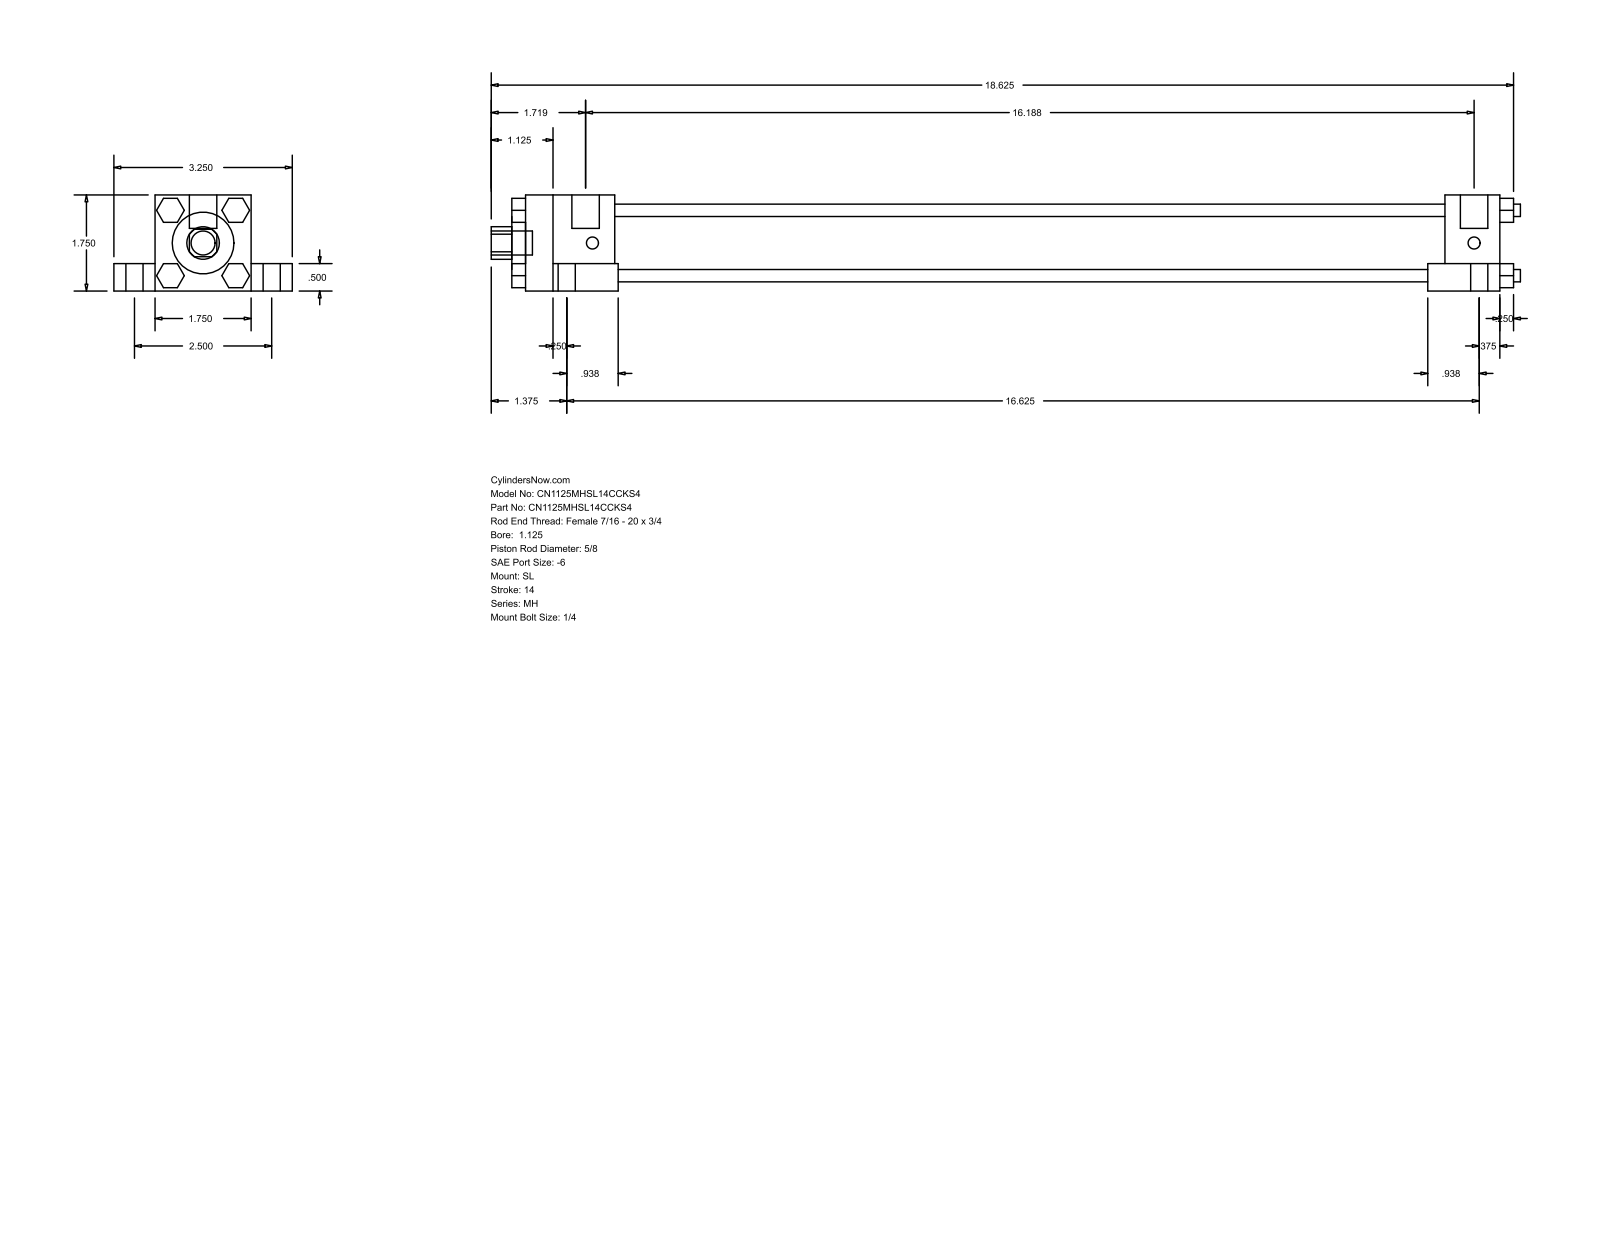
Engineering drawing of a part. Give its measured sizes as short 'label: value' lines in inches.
name: MH_SL__0112_0.625
written by: GSSL Pune (CONFIG_CONTROL_DESIGN)
unit: in
bodies: 0 solids, 150 faces (114 planar, 36 cylindrical, 0 other)
size: 18.75 × 3.25 × 1.75
holes: 1× ⌀0.625, 1× ⌀1.125, 1× ⌀1.375
bosses: 4× ⌀0.563, 4× ⌀0.313, 4× ⌀0.225, 4× ⌀0.219, 2× ⌀0.5, 1× ⌀0.437
rounds: 1× R0.297
face distances: 1.75, 0.75, 0.5, 1.25, 2.5, 0.437, 1.313, 15.938, 15.125, 16.125
